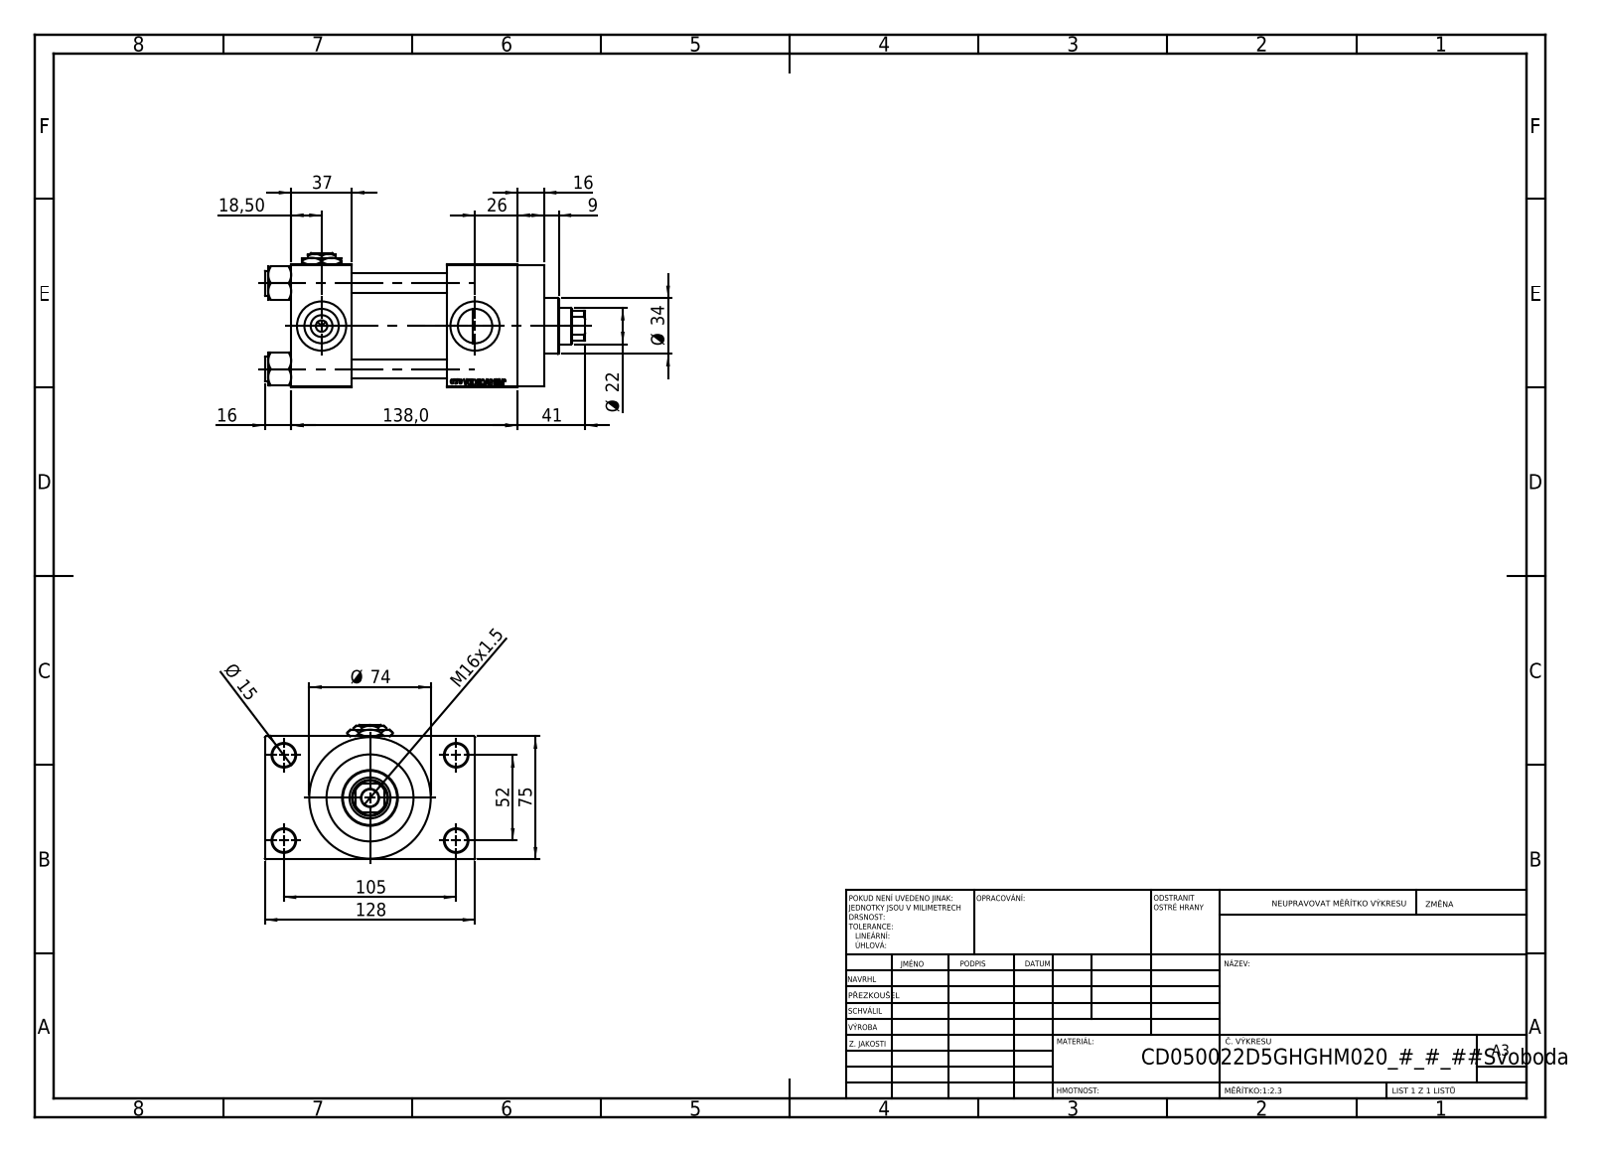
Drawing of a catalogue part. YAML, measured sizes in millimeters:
part_name: "V215CD_VC_A; Zatka_pro_OIL_PORT; V215CD_D_Body; V215CD_NUT_M5_D (+2 more)"
step_written_by: "SolidWorks 2019 (CONFIG_CONTROL_DESIGN)"
units: millimeters
bodies: {solids: 12, faces: 1156, planar: 521, cylindrical: 95, other: 540}
overall_size: [195, 128, 82]
volume: 795346
surface_area: 169294
round_holes:
  - {diameter: 12, count: 4}
  - {diameter: 14, count: 4}
  - {diameter: 7, count: 3}
  - {diameter: 20.96, count: 3}
  - {diameter: 30, count: 3}
  - {diameter: 10.5, count: 1}
  - {diameter: 22, count: 1}
  - {diameter: 25, count: 1}
  - {diameter: 41, count: 1}
  - {diameter: 50, count: 1}
  - {diameter: 53, count: 1}
round_bosses_or_shafts:
  - {diameter: 15, count: 4}
  - {diameter: 74, count: 1}
  - {diameter: 56, count: 1}
  - {diameter: 34, count: 1}
partial_cylinders:
  - {radius: 10.5, count: 1}
face_to_face_distances: [75, 58, 37, 95, 26.5, 43, 138, 101, 101.5, 16]
hole_center_spacings: [26.35, 36.98, 52.3, 58.43, 58.59, 78.65, 94.37, 52]
